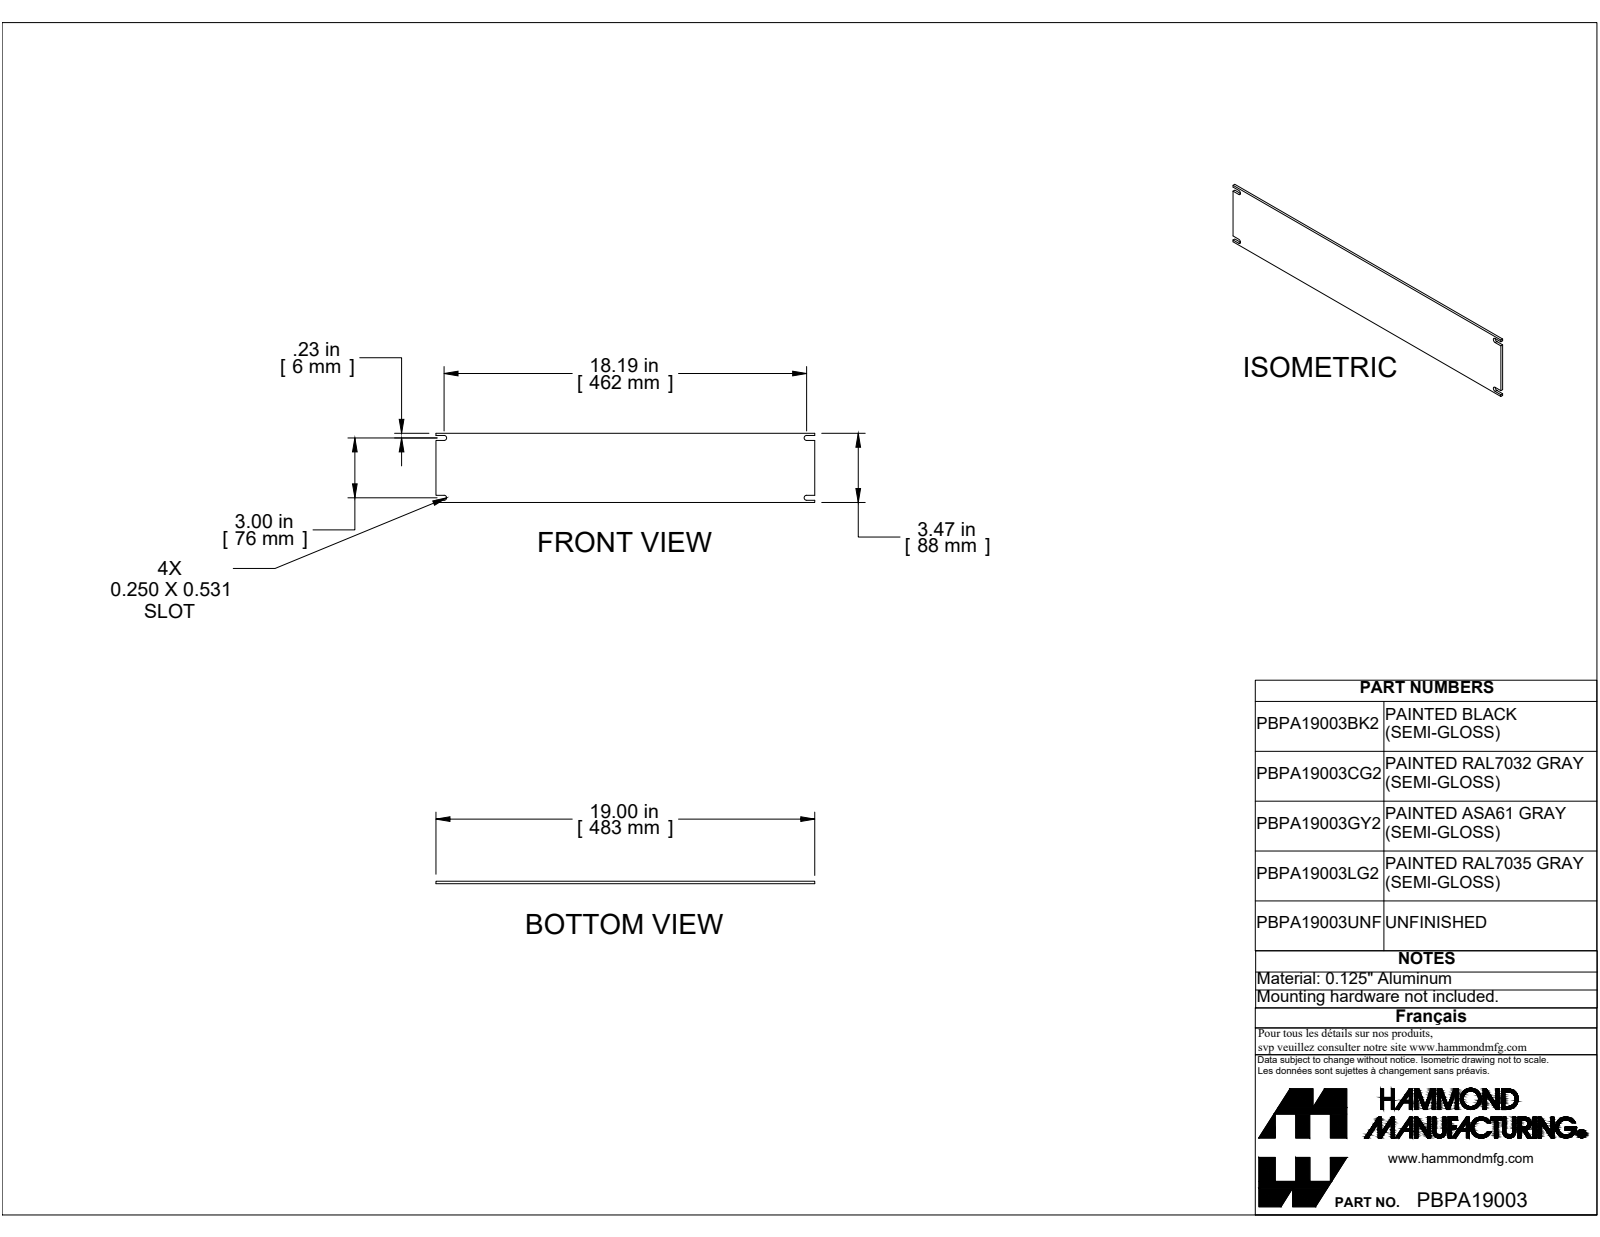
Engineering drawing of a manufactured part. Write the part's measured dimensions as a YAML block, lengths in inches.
part_name: "PBPA19003BK2"
step_written_by: "SolidWorks 2019 (CONFIG_CONTROL_DESIGN)"
units: inches
bodies: {solids: 1, faces: 22, planar: 18, cylindrical: 4, other: 0}
overall_size: [19, 3.468, 0.125]
volume: 8.173
surface_area: 136.9
partial_cylinders:
  - {radius: 0.125, count: 4}
face_to_face_distances: [0.125, 3.468, 19, 0.109, 0.359, 3.109, 3.359, 3, 0.25, 3.25]
